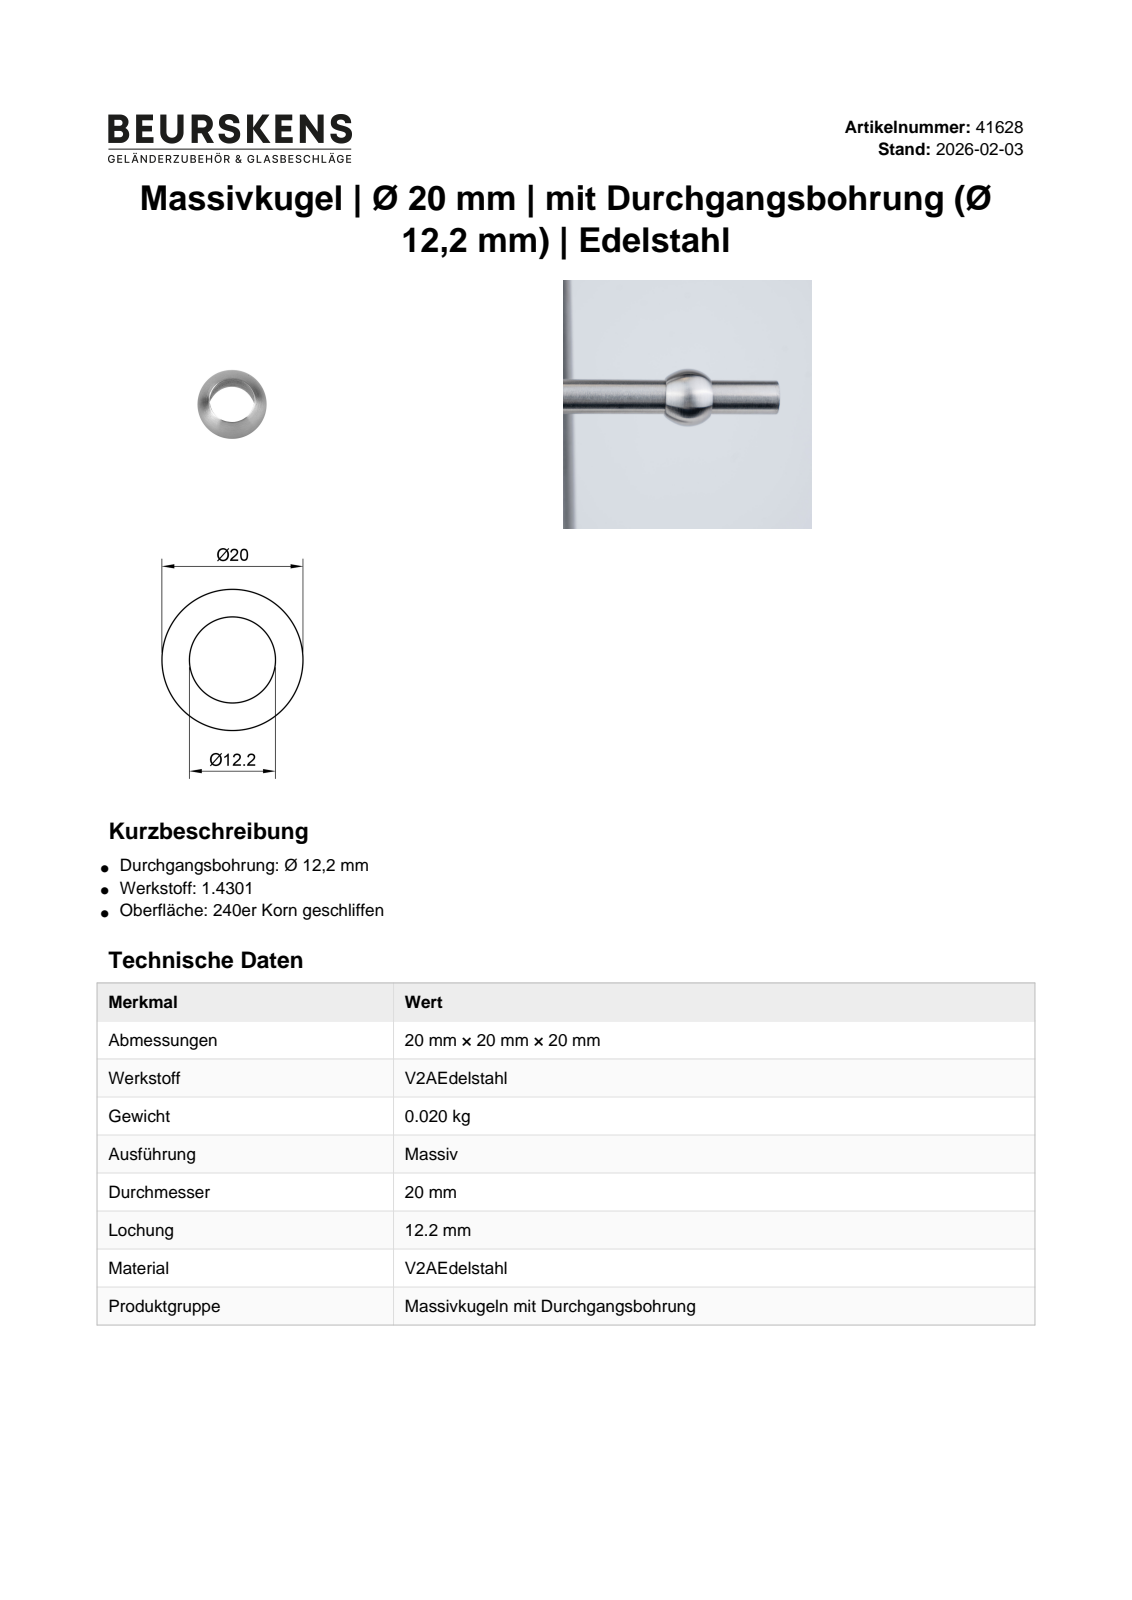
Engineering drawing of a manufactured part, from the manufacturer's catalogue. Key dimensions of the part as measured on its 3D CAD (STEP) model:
Part name (STEP PRODUCT): 41628
STEP written by: Autodesk Inventor 2022 (AUTOMOTIVE_DESIGN)
Units: millimetres
Bodies: 1 solid, 2 faces (0 planar, 1 cylindrical, 1 other)
Overall size (bounding box): 20 × 20 × 15.85
Volume: 2 084 mm³ · Surface area: 1 603 mm²
Round holes (diameter × count): ⌀12.2 ×1
